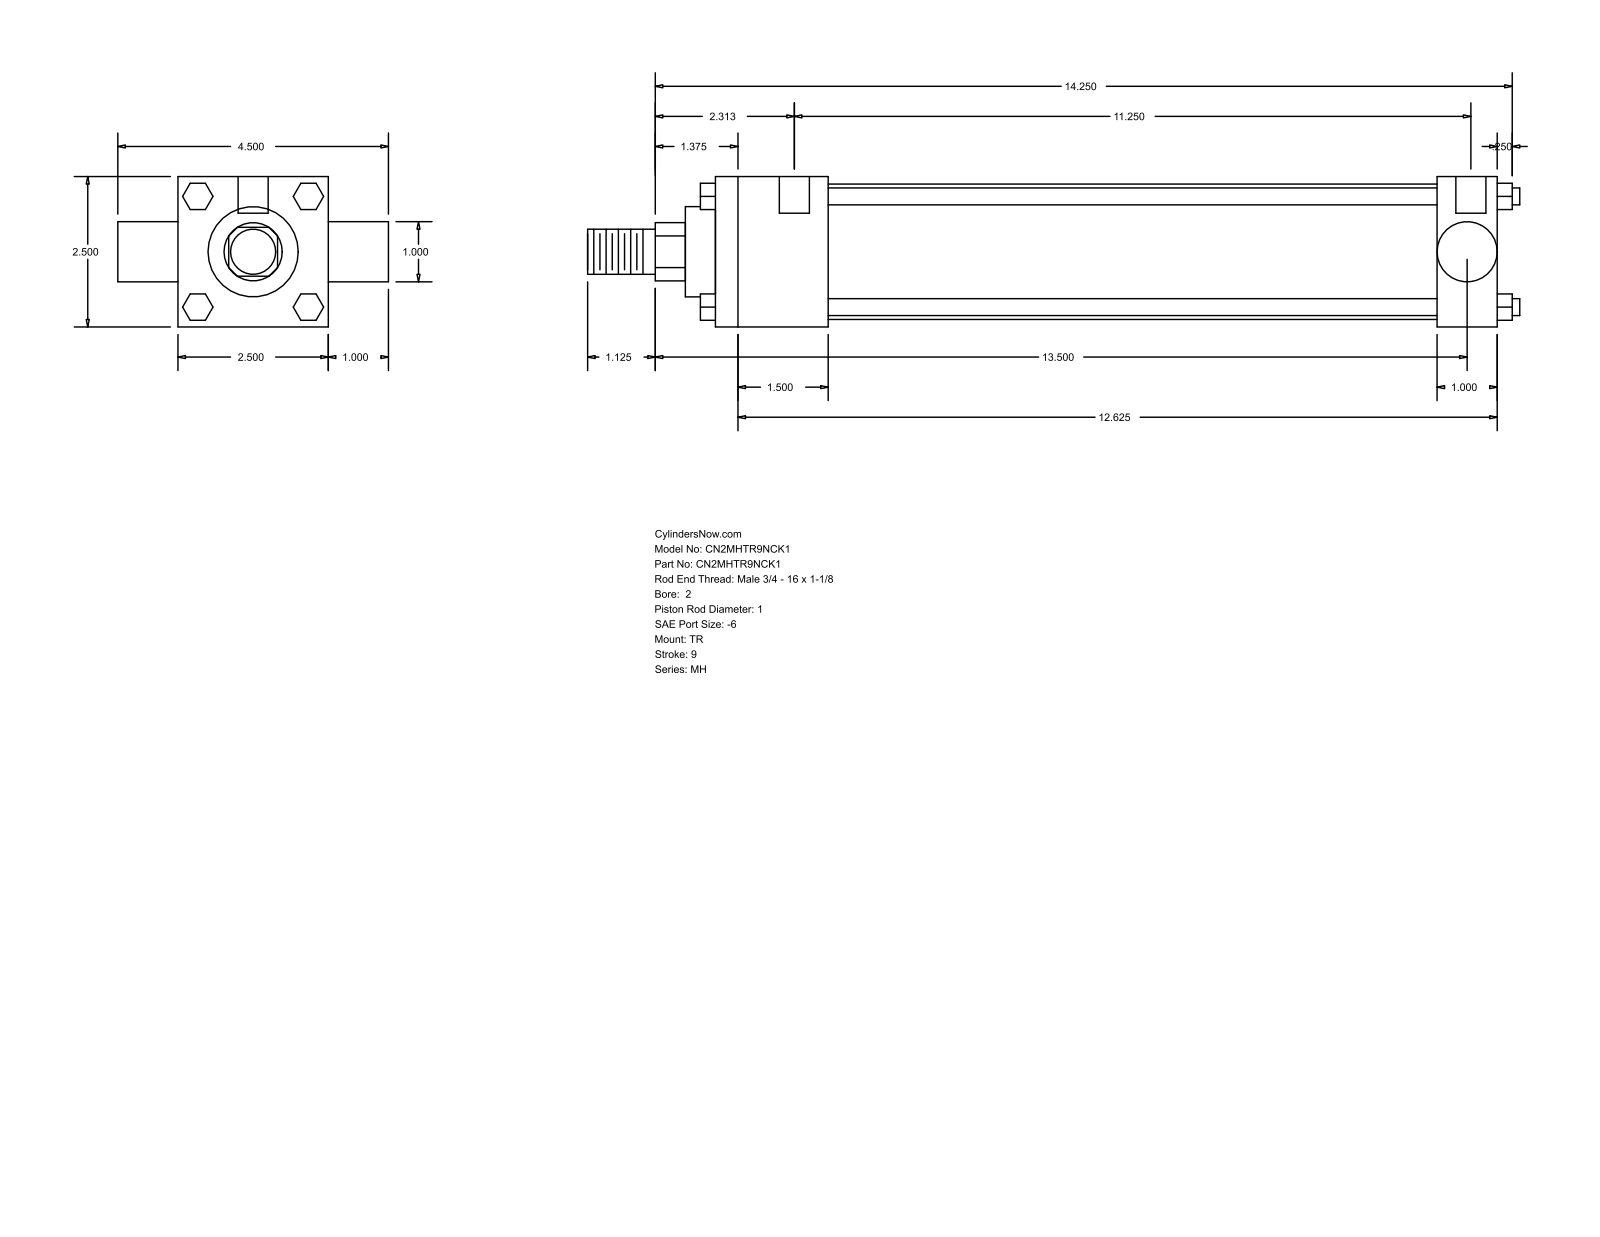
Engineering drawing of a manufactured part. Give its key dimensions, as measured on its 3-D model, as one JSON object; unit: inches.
{"part_name": "MH_TR__0200_1", "step_written_by": "GSSL Pune (CONFIG_CONTROL_DESIGN)", "units": "inches", "bodies": {"solids": 0, "faces": 120, "planar": 92, "cylindrical": 28, "other": 0}, "overall_size": [15.5, 4.5, 2.5], "round_holes": [[0.219, 3], [0.5, 2]], "round_bosses_or_shafts": [[0.281, 4], [2.25, 1], [1.5, 1], [1, 1], [0.998, 1], [0.75, 1]], "partial_cylinders_radius": [[0.484, 1]], "face_to_face_distances": [2.5, 13, 1, 1.875, 12, 10.125, 11.125, 3.5, 13.5, 0.25], "hole_center_spacings": [0.125, 0.187, 11.25, 11.375, 11.437, 11.562]}
